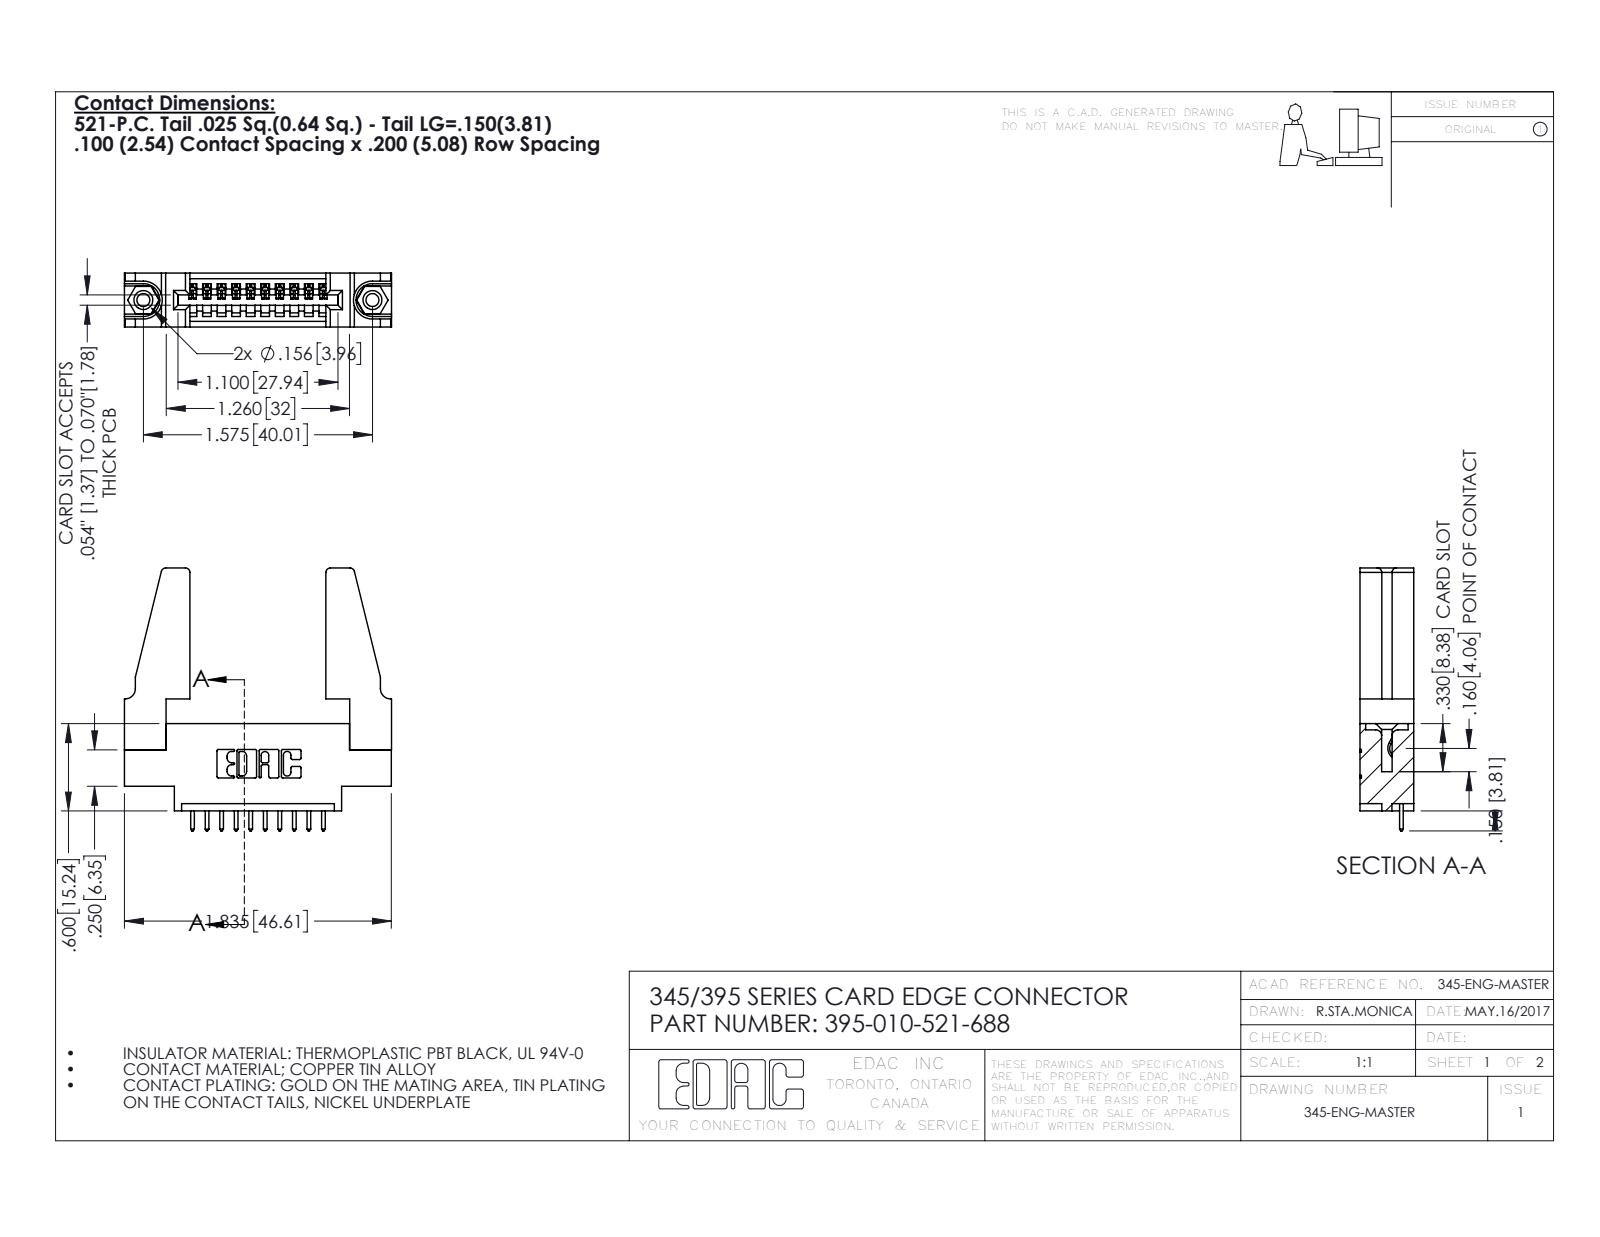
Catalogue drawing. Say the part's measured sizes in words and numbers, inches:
The part is named "345-292-001_345-293-121; 345-220-078_345-220-088; 395-010-521-688; 345 Part_0.170 Offset - 0.156 Dia-TH (+1 more)". Its 3-D file was written by "SolidWorks 2016 (CONFIG_CONTROL_DESIGN)". It is 15 solids with 834 faces: 556 planar, 262 cylindrical and 16 other. Overall it measures 1.836 by 1.807 by 0.37 inches. Its volume is 0.444 cubic inches and its surface area 12.49 square inches. Round holes: 2 of diameter 0.089, 2 of diameter 0.125, 2 of diameter 0.156, 1 of diameter 0.064. Round bosses or shafts: 2 of diameter 0.155. Partial cylindrical surfaces (rounded edges, fillets, slot ends): 22 of radius 0.01, 20 of radius 0.006, 20 of radius 0.01, 8 of radius 0.03, 6 of radius 0.007, 6 of radius 0.031, 3 of radius 0.026, 2 of radius 0.031. The main face-to-face distances are 0.37, 0.072, 0.298, 0.2, 0.098, 0.272, 0.025, 0.148, 0.15, 0.225. The hole center spacings are 0.27, 1.344, 1.575.
